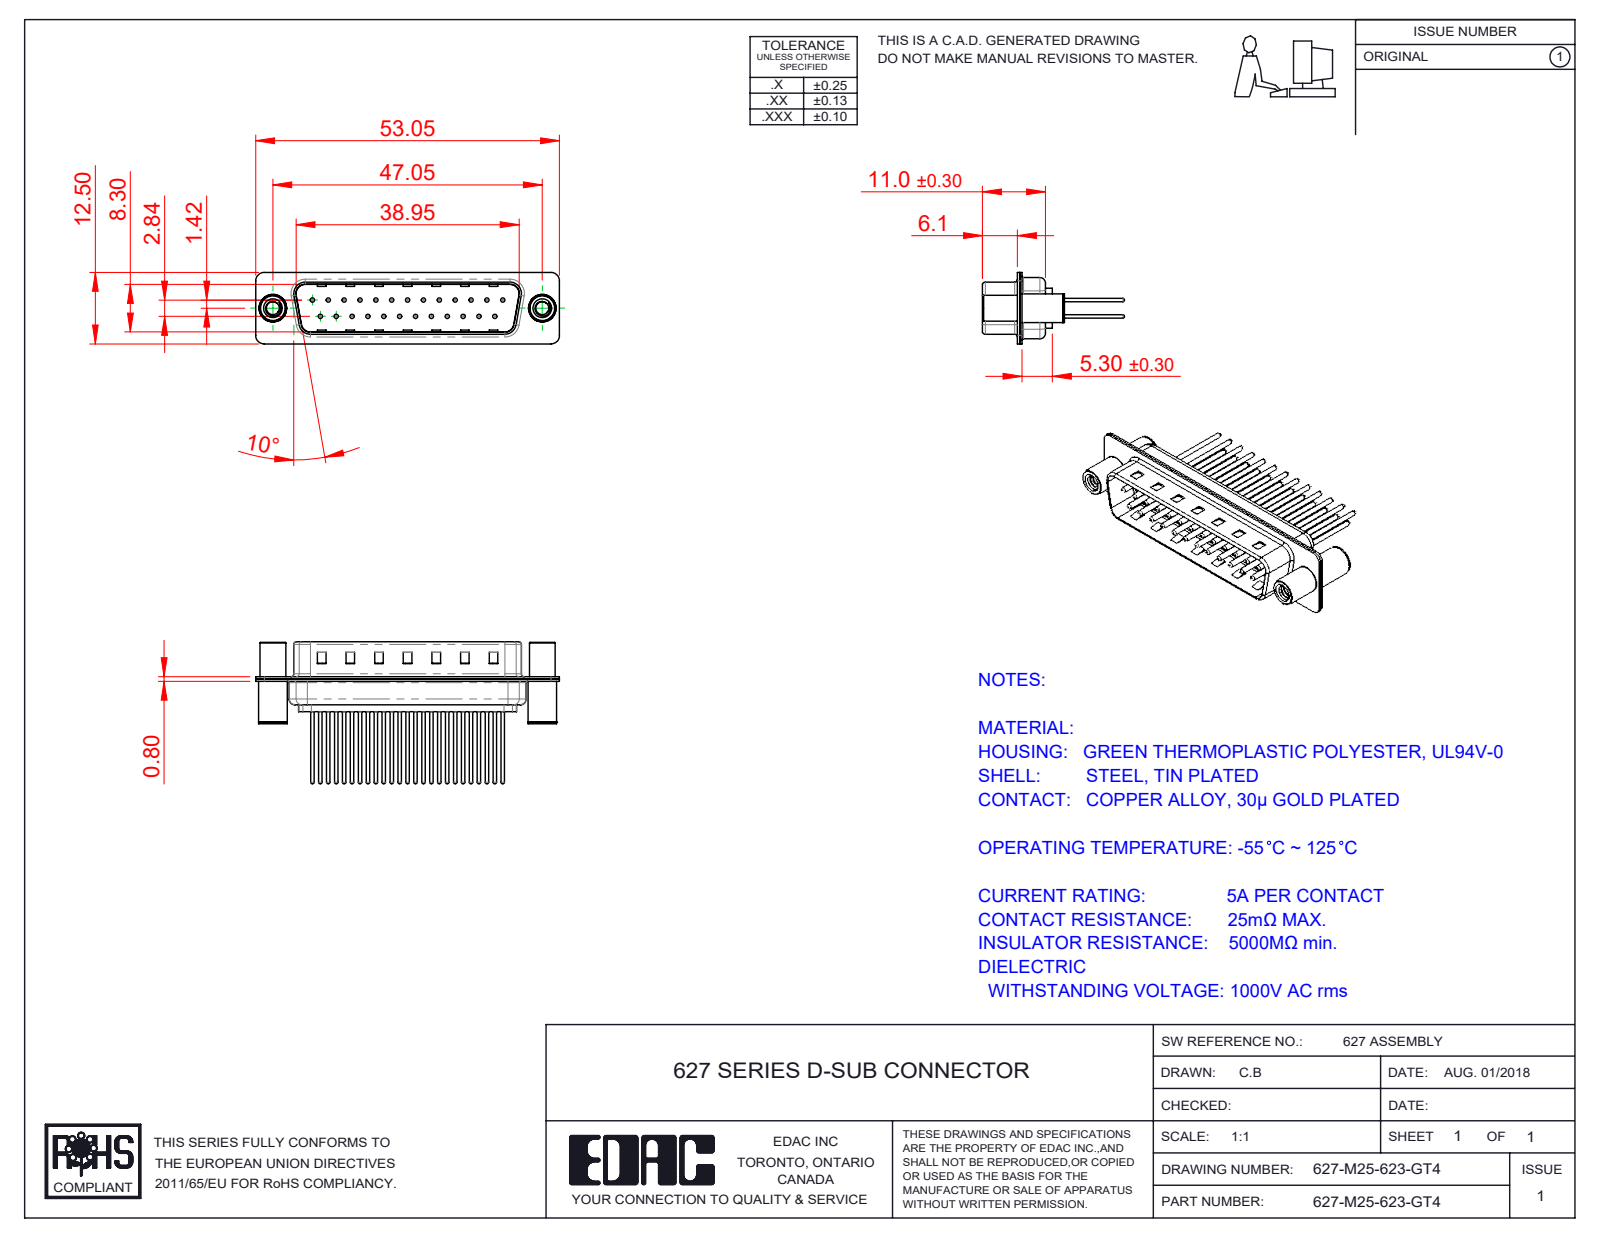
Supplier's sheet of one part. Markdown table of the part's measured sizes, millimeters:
| quantity | value |
| --- | --- |
| part name | 627-M25-623-GT4; 627M Housing_25 Contacts; 627M Shell Front_25 Contacts; 627M Contact Row 1_23 (+3 more) |
| STEP written by | SolidWorks 2020 (CONFIG_CONTROL_DESIGN) |
| units | millimeters |
| bodies | 30 solids, 1387 faces (352 planar, 539 cylindrical, 496 other) |
| overall size | 53.05 × 24.77 × 12.5 |
| volume | 3 055 mm³ |
| surface area | 7 696 mm² |
| round holes (diameter × count) | 0.75 × 25, 1.6 × 25, 2 × 25, 2.26 × 2, 3.26 × 2, 4 × 2, 4.8 × 2 |
| round bosses / shafts (diameter × count) | 1.5 × 25, 0.6 × 25, 5 × 2, 4.9 × 2, 4.5 × 2 |
| partial cylindrical surfaces (radius × count) | 1.5 × 16, 2 × 12, 0.5 × 8, 1.6 × 8, 0.25 × 4, 0.6 × 4, 0.65 × 4, 0.9 × 4 |
| main face-to-face distances | 0.4, 0.8, 9.5, 9.1, 8.7, 9.9, 1.2, 5.7, 6.1, 0.75 |
| hole center spacings | 3.16, 2.77, 5.54, 8.31, 11.08, 13.85, 16.62, 5.03 |
